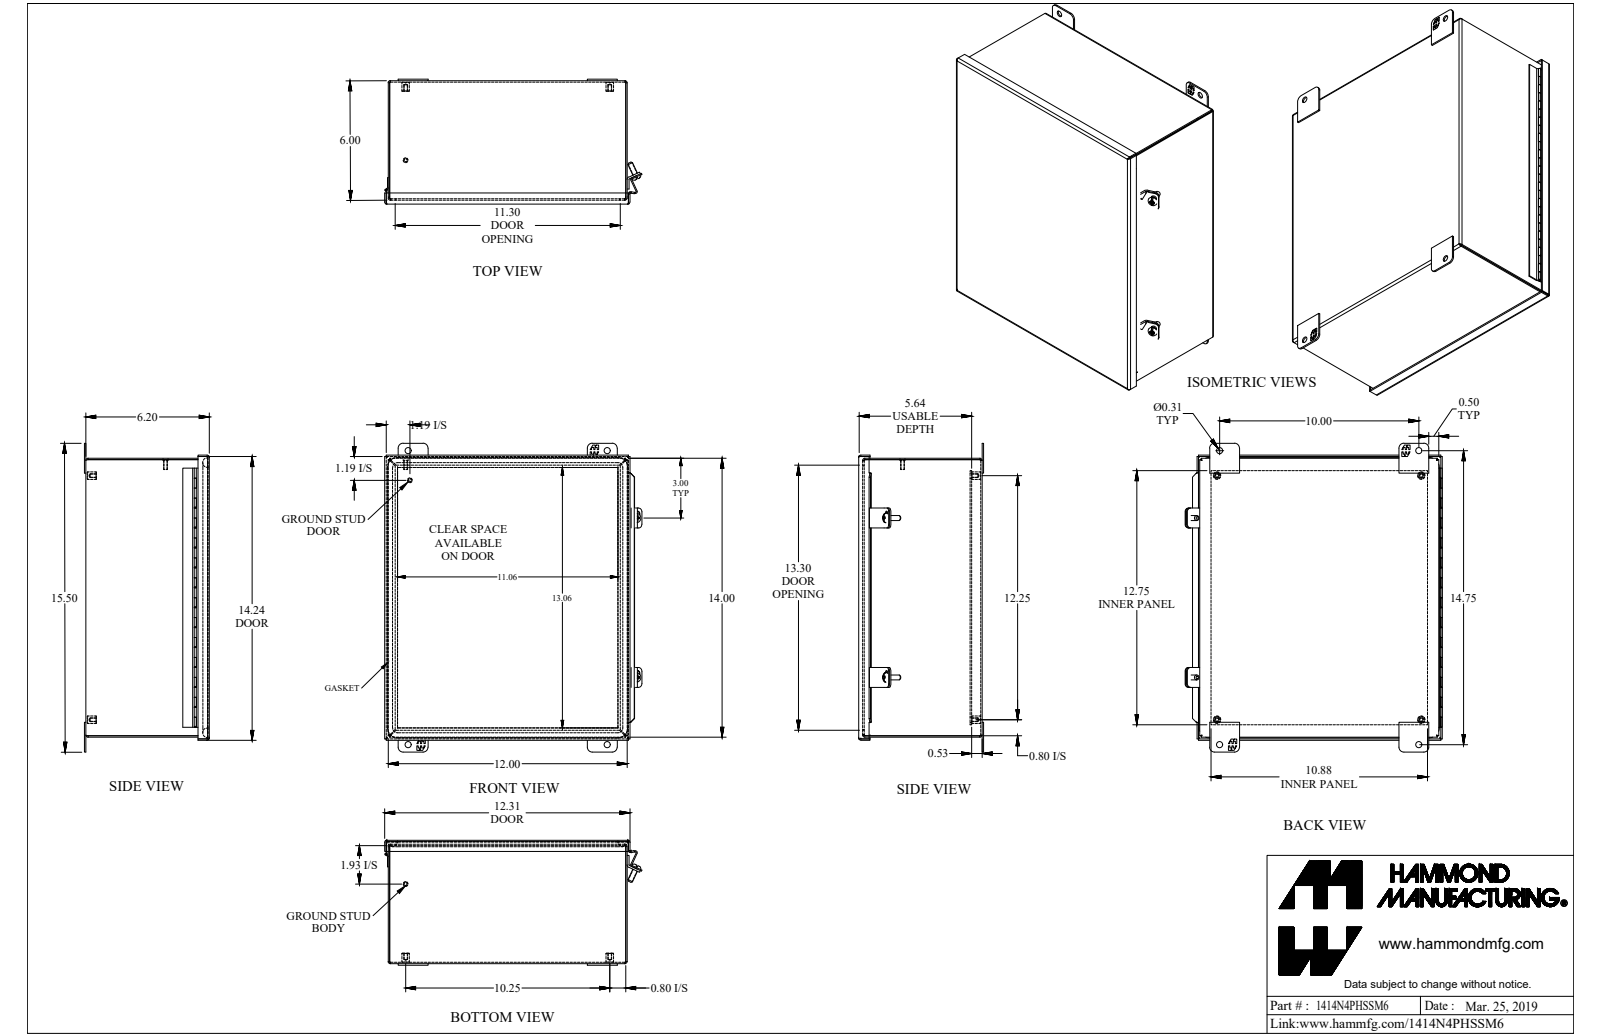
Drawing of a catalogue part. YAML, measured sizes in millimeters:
part_name: "1414N4PHSSM6"
step_written_by: "SolidWorks 2018 (AUTOMOTIVE_DESIGN)"
units: millimeters
bodies: {solids: 21, faces: 734, planar: 474, cylindrical: 200, other: 60}
overall_size: [393.7, 327.7, 159.2]
volume: 2470000
surface_area: 1182000
round_holes:
  - {diameter: 4, count: 4}
  - {diameter: 6.7, count: 4}
  - {diameter: 8, count: 4}
  - {diameter: 5.4, count: 2}
  - {diameter: 1.3, count: 1}
round_bosses_or_shafts:
  - {diameter: 9.5, count: 4}
  - {diameter: 6.4, count: 4}
  - {diameter: 12.2, count: 2}
  - {diameter: 4.8, count: 2}
  - {diameter: 2.5, count: 1}
  - {diameter: 1.1, count: 1}
partial_cylinders:
  - {radius: 6.4, count: 24}
  - {radius: 0.9, count: 9}
  - {radius: 2.7, count: 9}
  - {radius: 4.8, count: 8}
  - {radius: 2, count: 4}
  - {radius: 3, count: 4}
  - {radius: 3.6, count: 4}
  - {radius: 12.7, count: 4}
face_to_face_distances: [1.8, 13.5, 143.1, 14.3, 157.4, 155.6, 141.3, 303, 15.3, 143.9]
hole_center_spacings: [259.1, 405.7, 31.9, 342.9, 428.6, 260.4, 260.4, 311.2]
